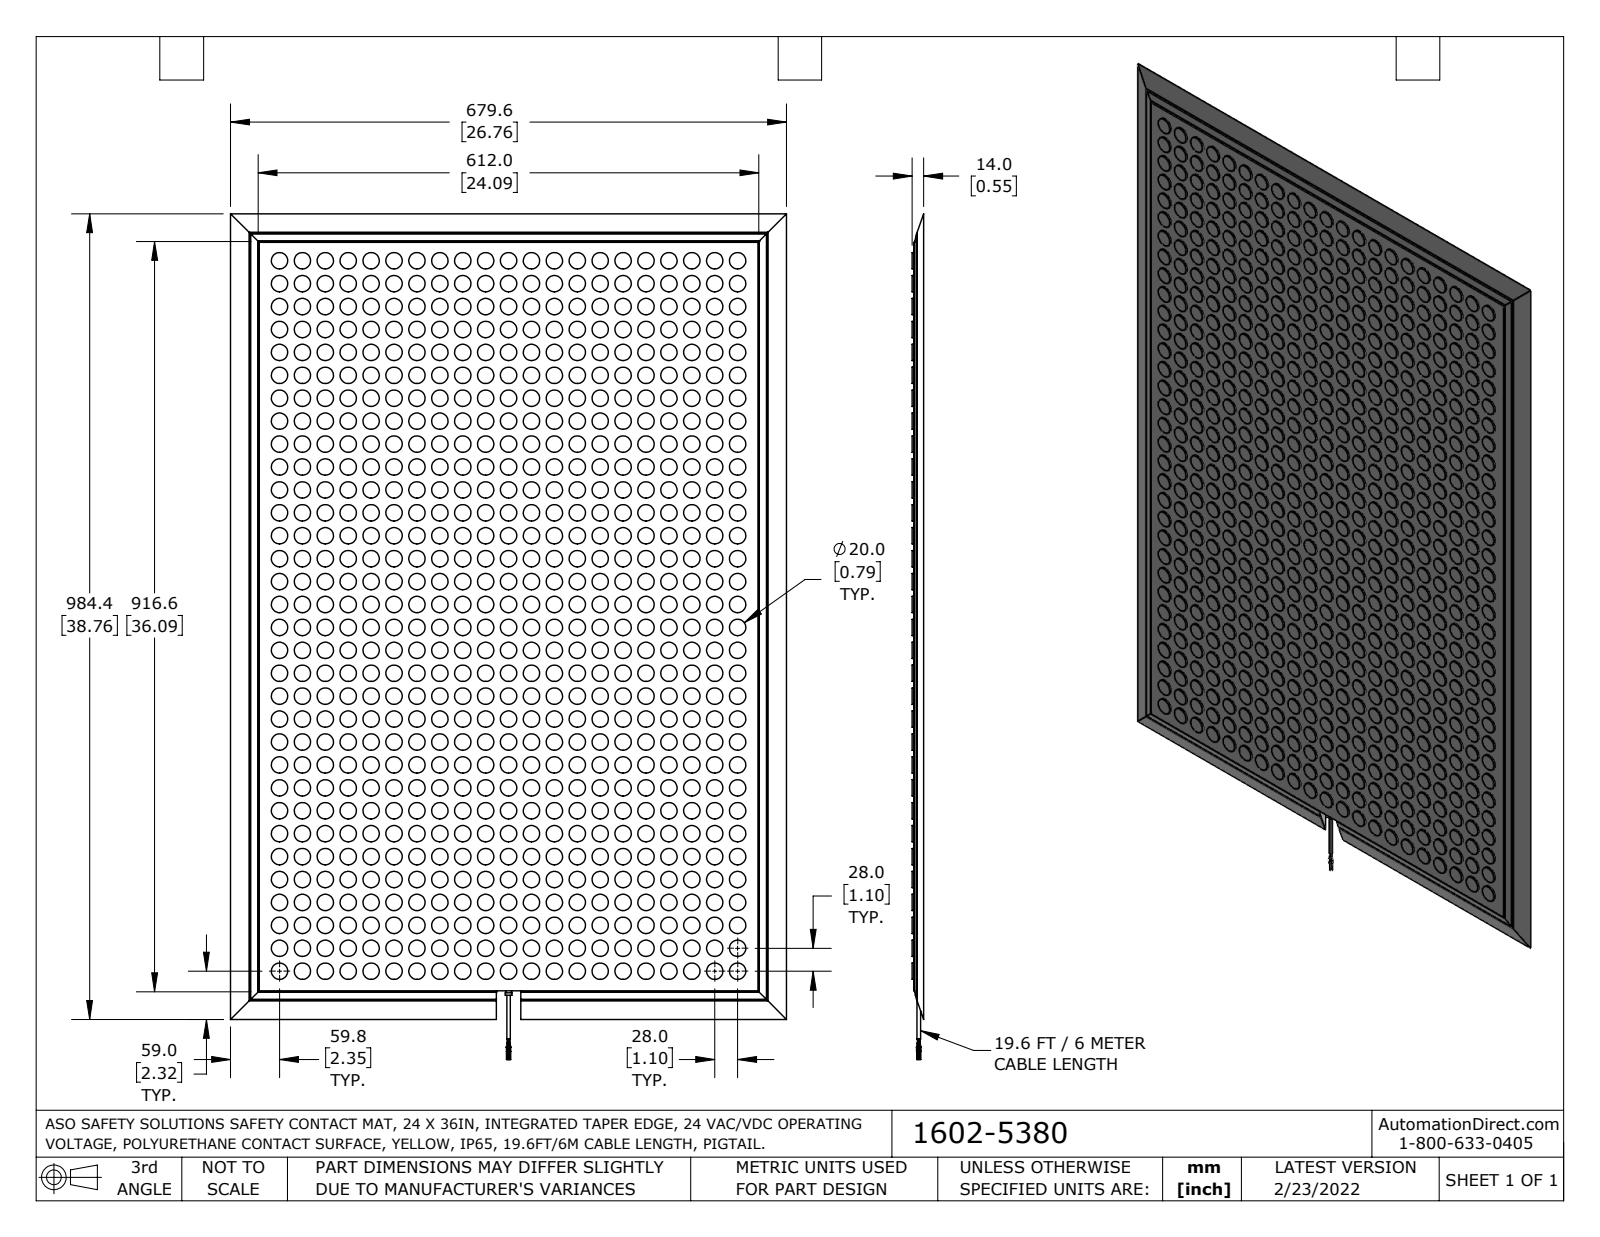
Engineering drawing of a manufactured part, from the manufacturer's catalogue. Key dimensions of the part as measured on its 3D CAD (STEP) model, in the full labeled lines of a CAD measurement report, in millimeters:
Part name (STEP PRODUCT): 1602-5380_Default
STEP written by: SolidWorks 2021 (CONFIG_CONTROL_DESIGN)
Units: millimetres
Bodies: 3 solids, 2189 faces (730 planar, 1427 cylindrical, 32 other)
Overall size (bounding box): 1033.4 × 679.6 × 14
Volume: 7 743 000 mm³ · Surface area: 1 465 000 mm²
Round holes (diameter × count): ⌀4.4 ×1
Round bosses / shafts (diameter × count): ⌀20 ×672, ⌀1.2 ×20, ⌀0.8 ×8, ⌀8 ×1, ⌀7 ×1
Partial cylindrical surfaces — rounded edges, fillets, slot ends (radius × count): R0.2 ×4
Main face-to-face distances: 12, 14, 2, 6, 609.6, 914.4, 8, 289.8, 319.8, 30
